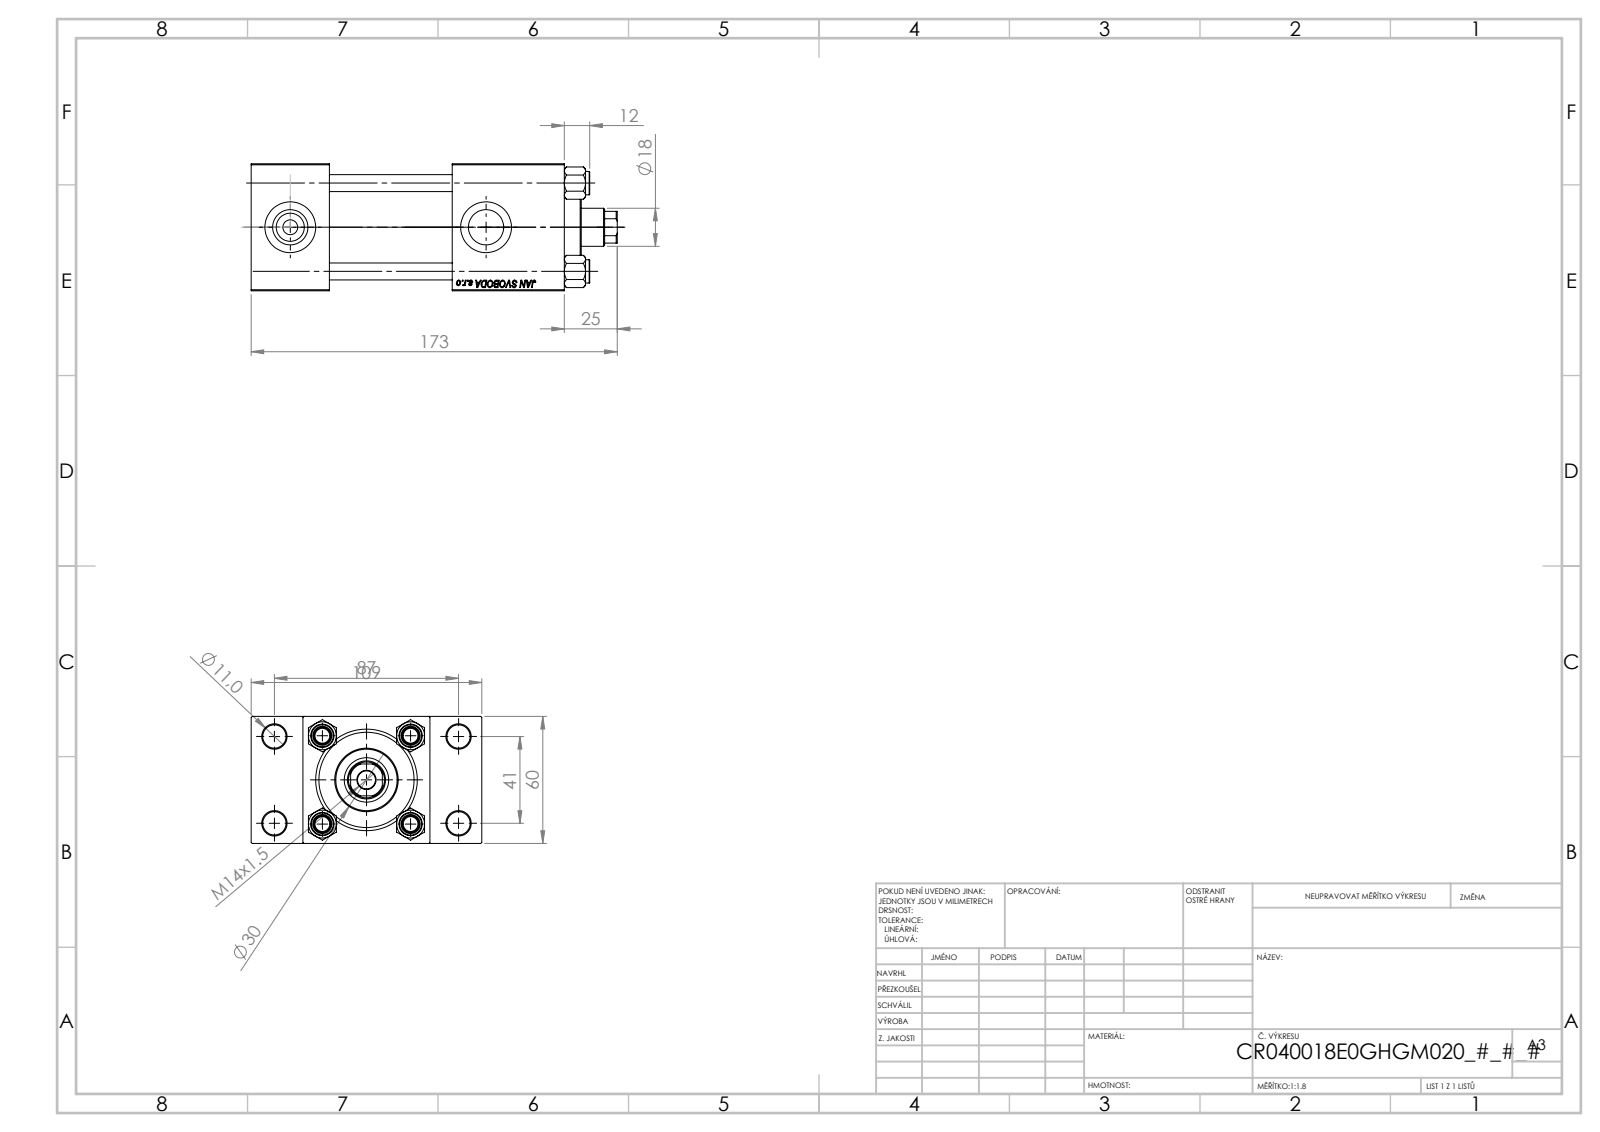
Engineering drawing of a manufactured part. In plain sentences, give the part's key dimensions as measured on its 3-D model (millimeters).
The part is named "NUT_M5_E; V215CR_E_Body; V215_VC_A; V215CR_TYCINKA_E (+1 more)". Its 3-D file was written by "SolidWorks 2019 (CONFIG_CONTROL_DESIGN)". It is 11 solids with 1136 faces: 498 planar, 86 cylindrical and 552 other. Overall it measures 173 by 109 by 60 millimeters. Its volume is 499 524 cubic millimeters and its surface area 124 461 square millimeters. Round holes: 4 of diameter 8, 4 of diameter 11, 2 of diameter 7, 2 of diameter 16.66, 2 of diameter 24, 1 of diameter 8.5, 1 of diameter 18, 1 of diameter 21, 1 of diameter 31, 1 of diameter 40, 1 of diameter 45. Round bosses or shafts: 4 of diameter 11, 1 of diameter 46, 1 of diameter 30. Partial cylindrical surfaces (rounded edges, fillets, slot ends): 1 of radius 8.5. The main face-to-face distances are 60, 37, 24.5, 84.5, 148, 111, 24.3, 58, 53, 82.3. The hole center spacings are 22.65, 29.49, 41.7, 47.15, 48.09, 64.35, 76.49, 41.
